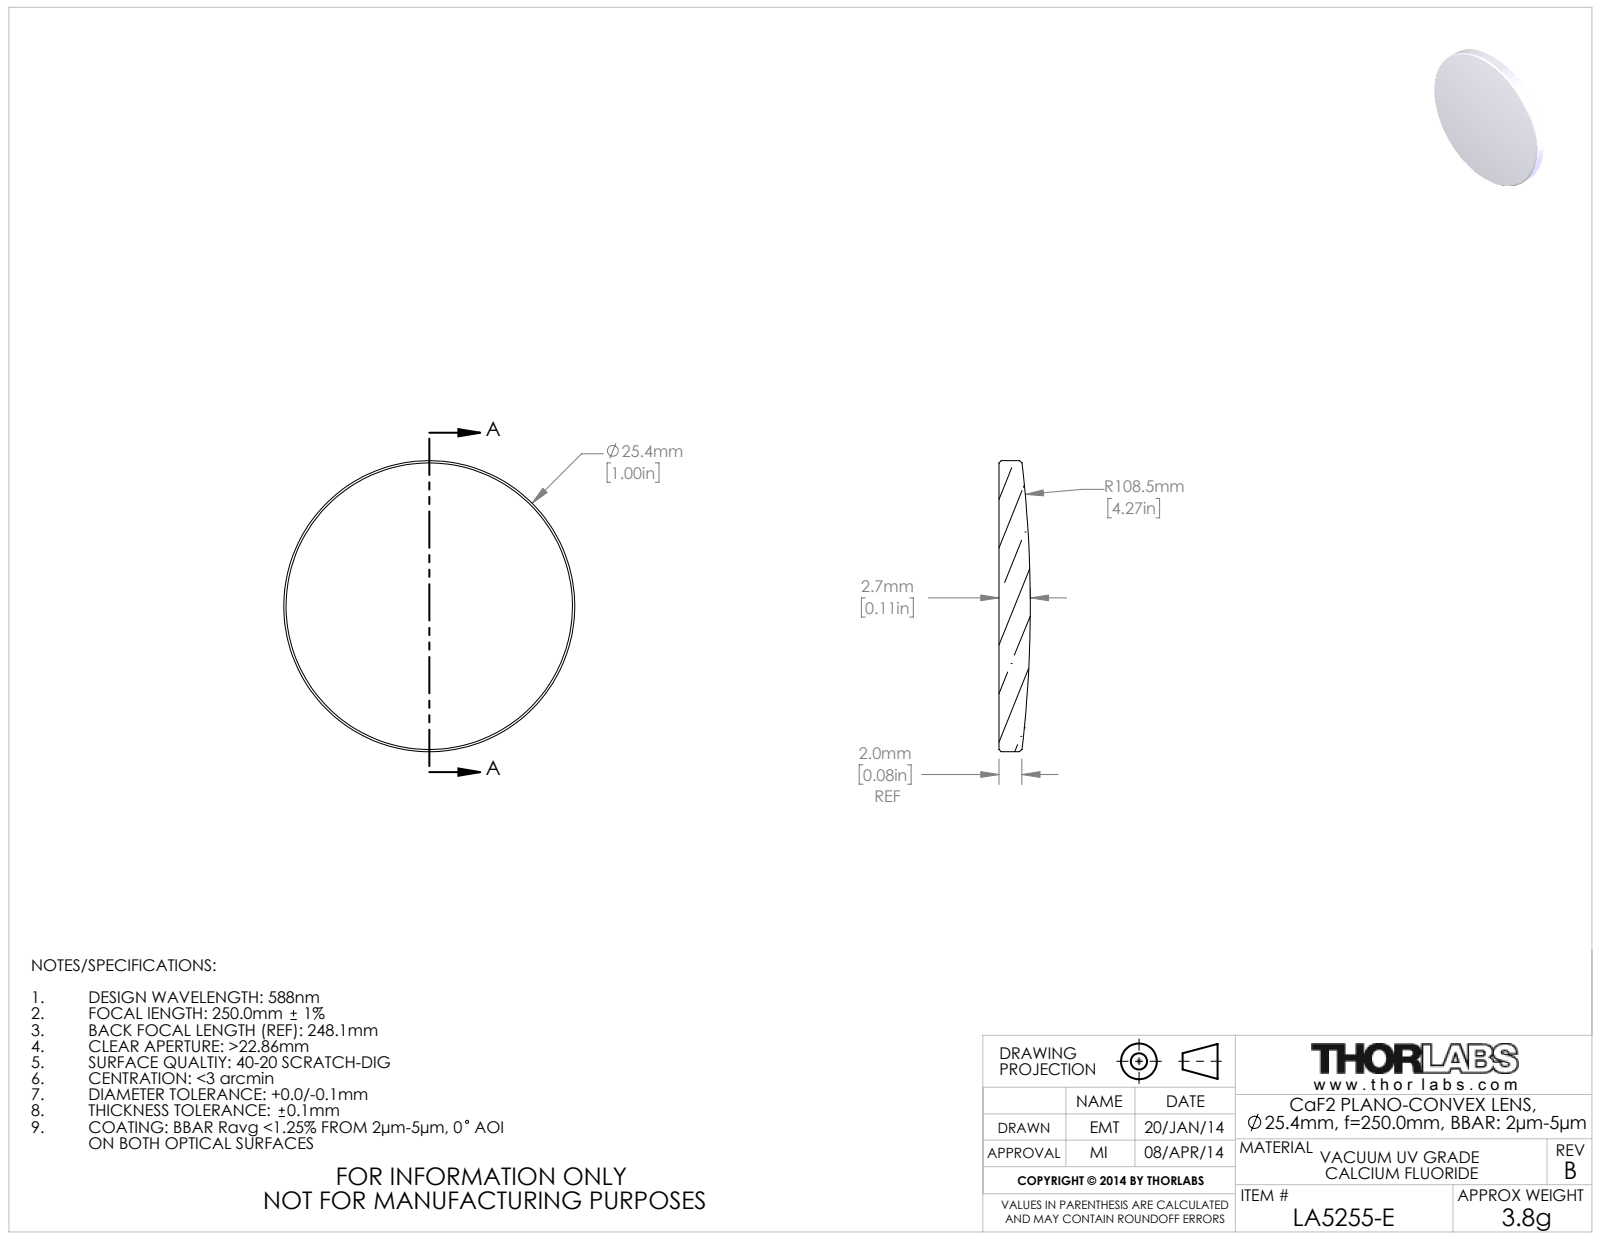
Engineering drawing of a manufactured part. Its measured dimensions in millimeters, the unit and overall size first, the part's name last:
Units: millimetres
Overall size (bounding box): 25.4 × 25.4 × 2.74
Round bosses / shafts (diameter × count): ⌀25.4 ×1
Volume: 1 196 mm³ · Surface area: 1 157 mm²
Bodies: 1 solid, 9 faces (1 planar, 2 cylindrical, 6 other)
Part name (STEP PRODUCT): 20137-E0W
STEP written by: SolidWorks 2018 (CONFIG_CONTROL_DESIGN)
